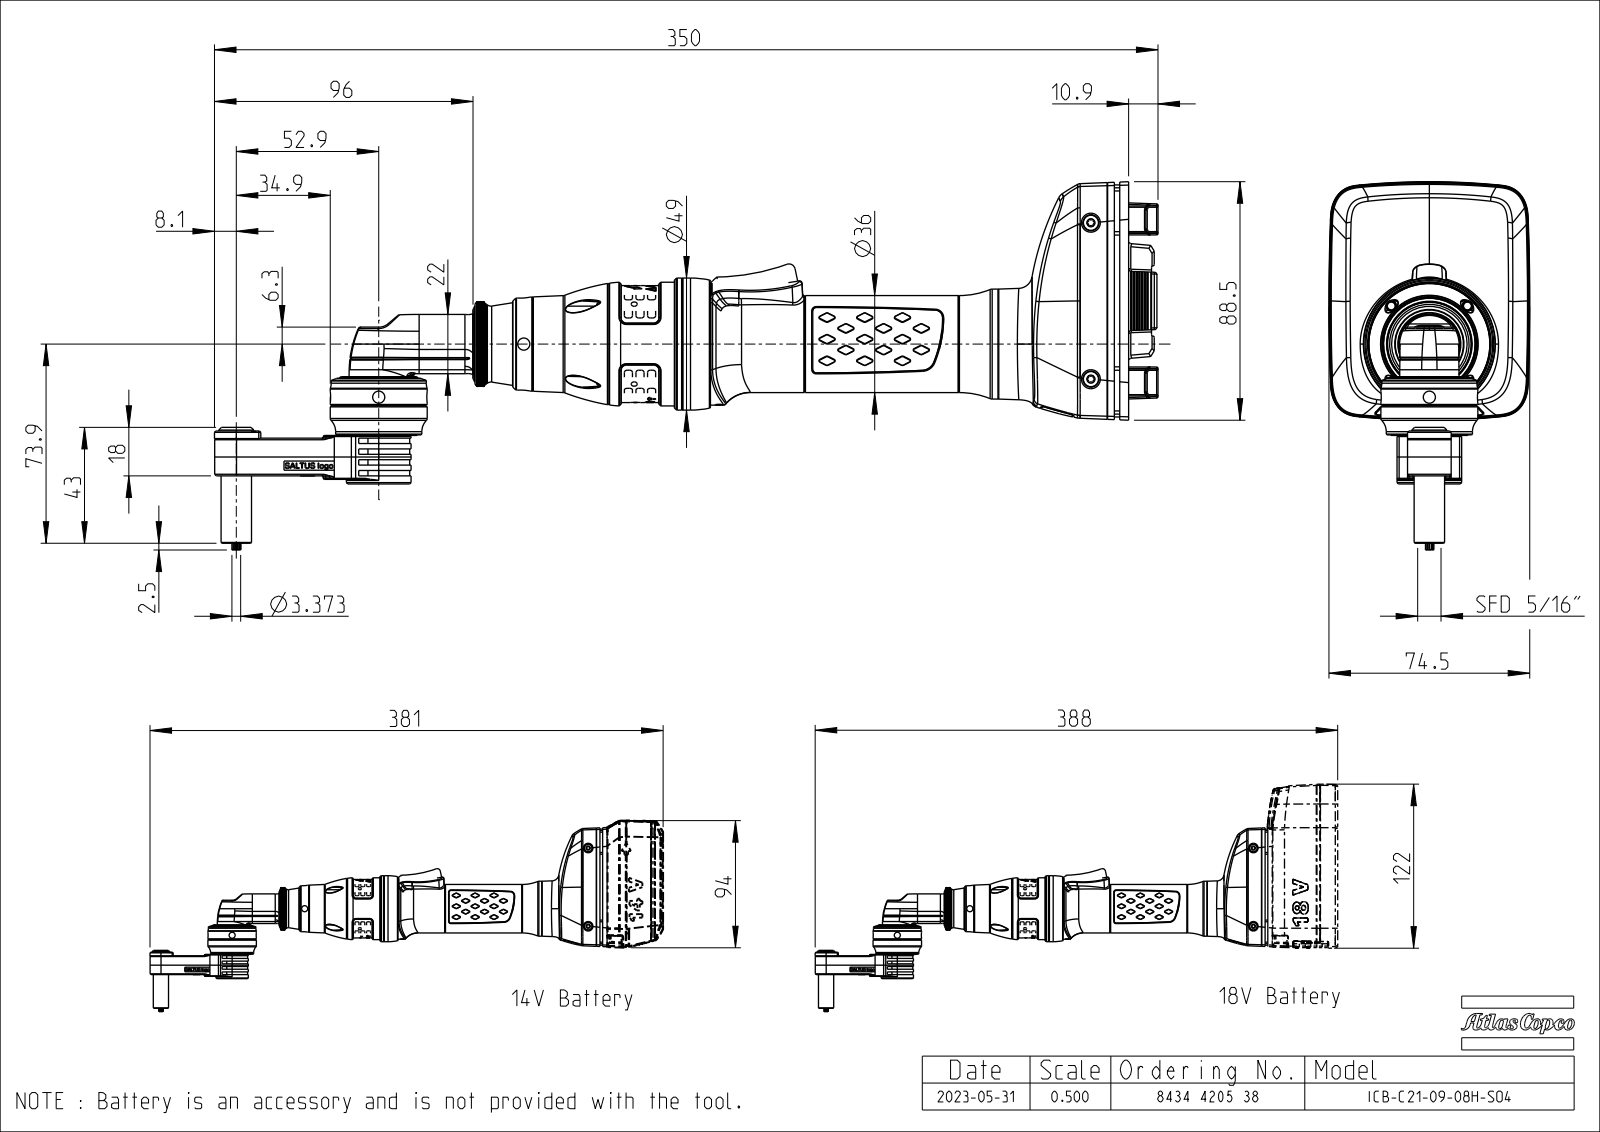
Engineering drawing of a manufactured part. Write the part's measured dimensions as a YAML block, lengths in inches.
part_name: "EXT_COMP_SW0007"
step_written_by: "CREO PARAMETRIC BY PTC INC, 2022414 (CONFIG_CONTROL_DESIGN)"
units: inches
bodies: {solids: 2, faces: 9753, planar: 6651, cylindrical: 1143, other: 1959}
overall_size: [13.791, 5.38, 2.935]
volume: 31.04
surface_area: 127.6
round_holes:
  - {diameter: 0.079, count: 4}
  - {diameter: 0.083, count: 4}
  - {diameter: 0.177, count: 4}
  - {diameter: 0.102, count: 2}
  - {diameter: 0.142, count: 2}
  - {diameter: 0.146, count: 2}
  - {diameter: 0.217, count: 2}
  - {diameter: 0.236, count: 2}
  - {diameter: 0.098, count: 1}
  - {diameter: 0.114, count: 1}
  - {diameter: 0.138, count: 1}
  - {diameter: 0.161, count: 1}
round_bosses_or_shafts:
  - {diameter: 0.315, count: 4}
  - {diameter: 0.22, count: 3}
  - {diameter: 1.417, count: 2}
  - {diameter: 0.138, count: 2}
  - {diameter: 1.929, count: 1}
  - {diameter: 1.866, count: 1}
  - {diameter: 1.807, count: 1}
  - {diameter: 1.783, count: 1}
partial_cylinders:
  - {radius: 0.02, count: 81}
  - {radius: 0.039, count: 67}
  - {radius: 0.012, count: 34}
  - {radius: 0.011, count: 30}
  - {radius: 0.02, count: 30}
  - {radius: 0.008, count: 24}
  - {radius: 0.015, count: 24}
  - {radius: 0.027, count: 24}
face_to_face_distances: [7.461, 7.524, 0.063, 0.118, 0.039, 4.744, 2.717, 2.78, 4.743, 2.718]
hole_center_spacings: [0.217, 0.306, 0.472, 0.159, 0.348, 0.348, 0.353, 0.353]
